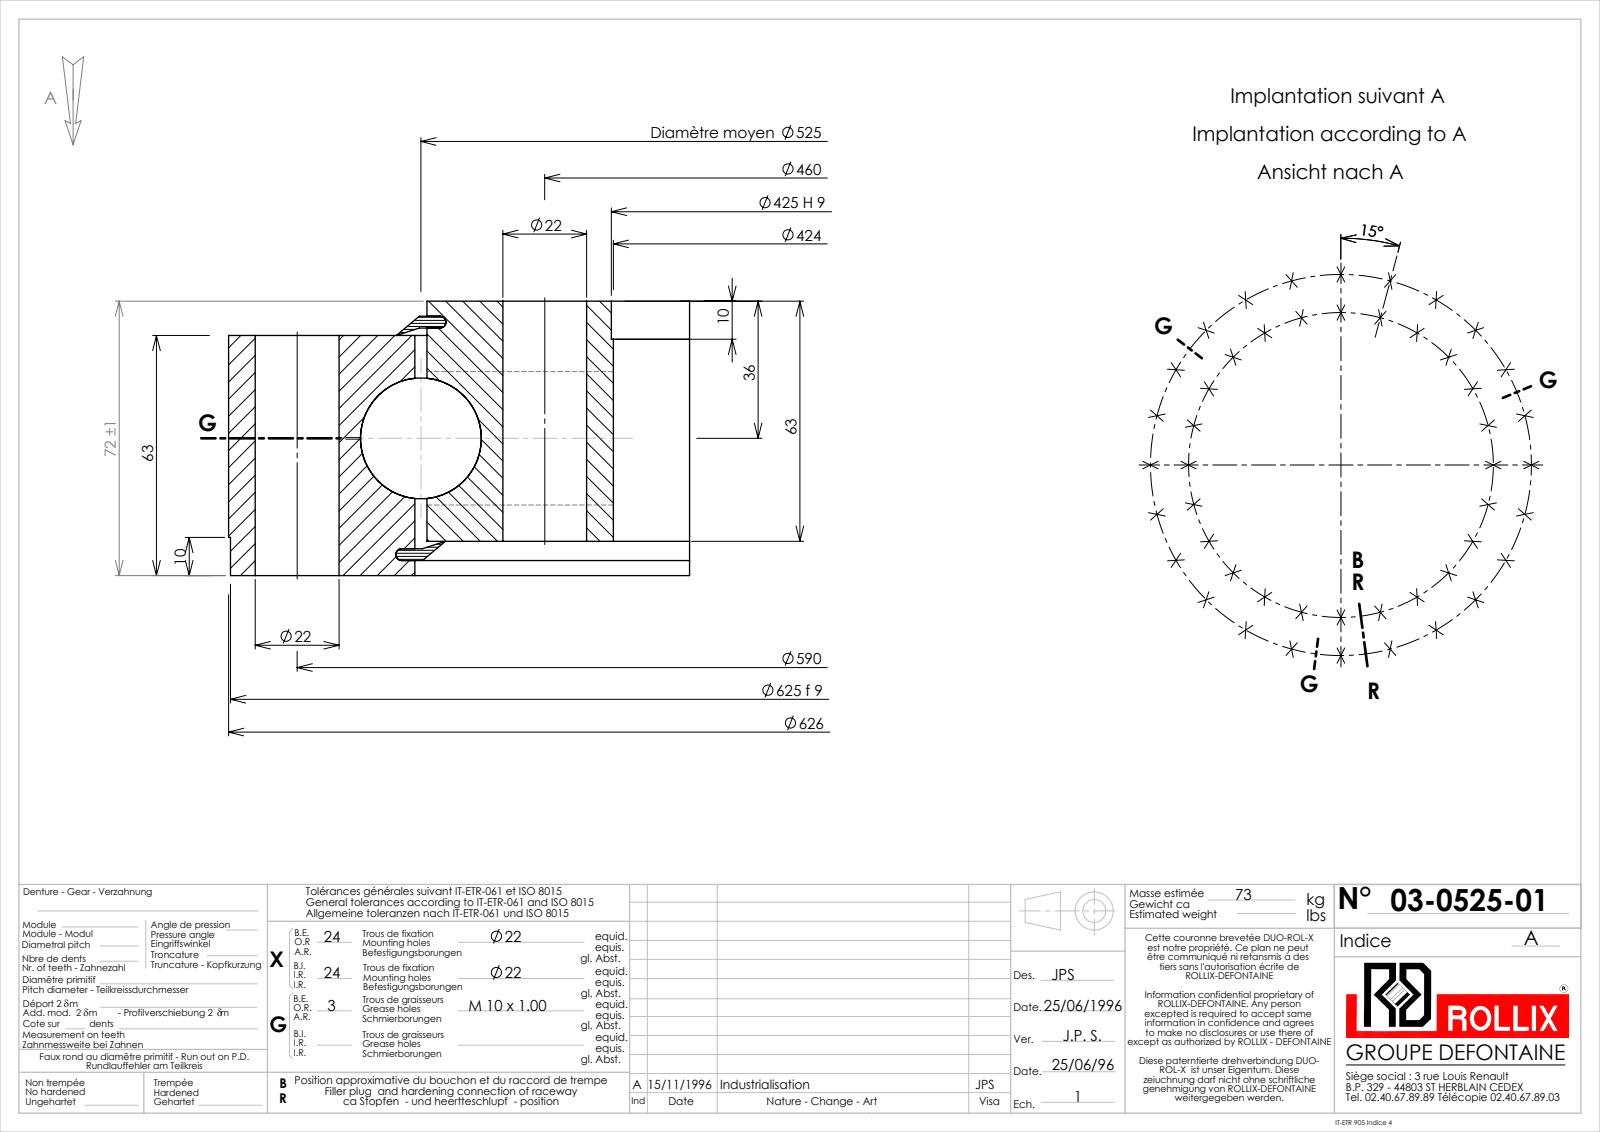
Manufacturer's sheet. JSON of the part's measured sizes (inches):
{"part_name": "03-0525-01", "step_written_by": "SolidWorks 2016 (CONFIG_CONTROL_DESIGN)", "units": "inches", "bodies": {"solids": 5, "faces": 164, "planar": 14, "cylindrical": 122, "other": 28}, "overall_size": [24.646, 24.646, 2.835], "volume_in3": 483.3, "surface_area_in2": 1696, "round_holes": [[0.866, 48], [0.354, 3], [16.693, 1], [16.732, 1], [20.794, 1]], "round_bosses_or_shafts": [[24.646, 1], [24.606, 1], [20.544, 1]], "face_to_face_distances": [2.48, 0.354, 2.126, 2.835, 0.156, 2.679, 0.199, 2.325, 0.278, 2.557], "hole_center_spacings": [9.055, 2.364, 11.025, 14.368, 12.806, 4.687, 6.93, 16.732]}
